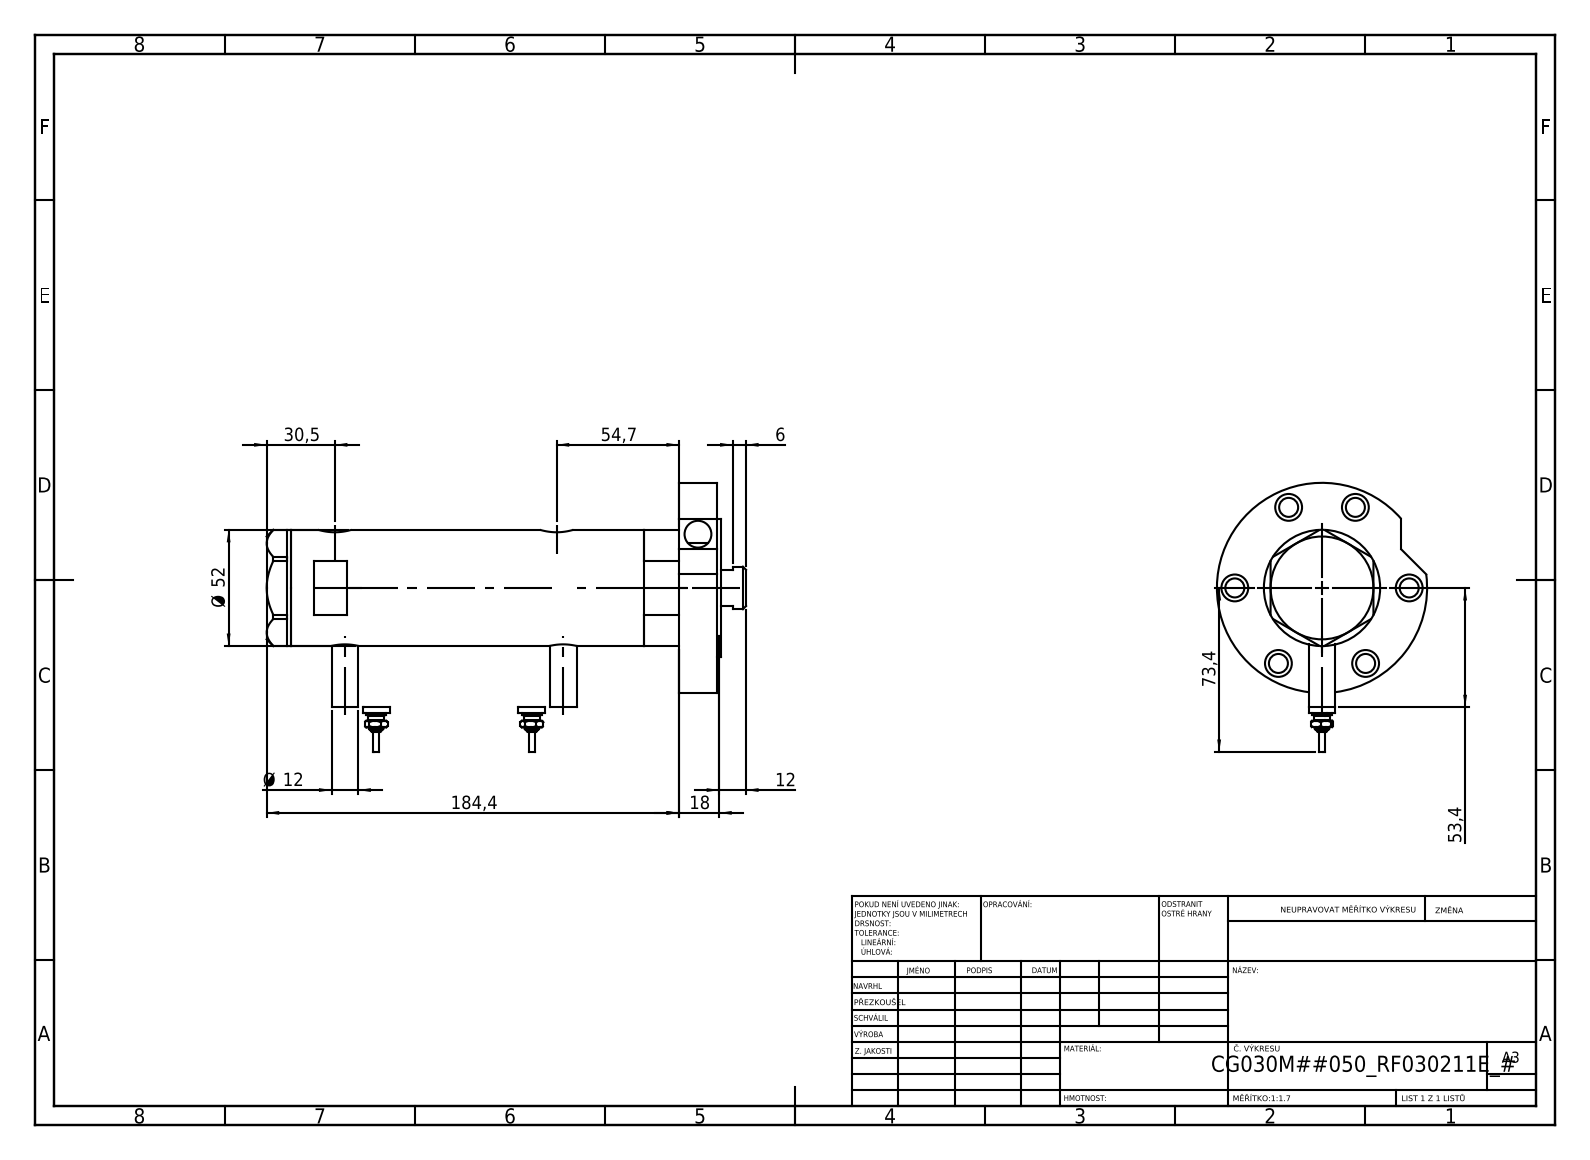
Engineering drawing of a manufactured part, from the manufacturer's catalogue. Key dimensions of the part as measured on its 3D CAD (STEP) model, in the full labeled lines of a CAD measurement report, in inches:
Part name (STEP PRODUCT): V270CG_RF211E; V270CG_VC; V270CG_FRONT; Switch (+2 more)
STEP written by: SolidWorks 2019 (CONFIG_CONTROL_DESIGN)
Units: inches
Bodies: 7 solids, 270 faces (104 planar, 102 cylindrical, 64 other)
Overall size (bounding box): 8.441 × 4.74 × 3.701
Volume: 29.21 in³ · Surface area: 176.1 in²
Round holes (diameter × count): ⌀0.472 ×7, ⌀0.335 ×6, ⌀0.383 ×2, ⌀0.492 ×2, ⌀0.591 ×2, ⌀0.256 ×1, ⌀0.787 ×1, ⌀0.846 ×1, ⌀1.181 ×1, ⌀1.299 ×1, ⌀1.575 ×1, ⌀1.732 ×1
Round bosses / shafts (diameter × count): ⌀0.472 ×4, ⌀0.354 ×2, ⌀0.276 ×2, ⌀0.177 ×2, ⌀0.098 ×2, ⌀3.701 ×1, ⌀2.441 ×1, ⌀2.047 ×1
Main face-to-face distances: 0.669, 6.827, 7.496, 0.079, 7.575, 4.783, 2.043, 2.713, 0.433, 8.008
Hole centre spacings: 1.535, 1.706, 2.553, 2.659, 2.754, 3.064, 0.114, 0.177
